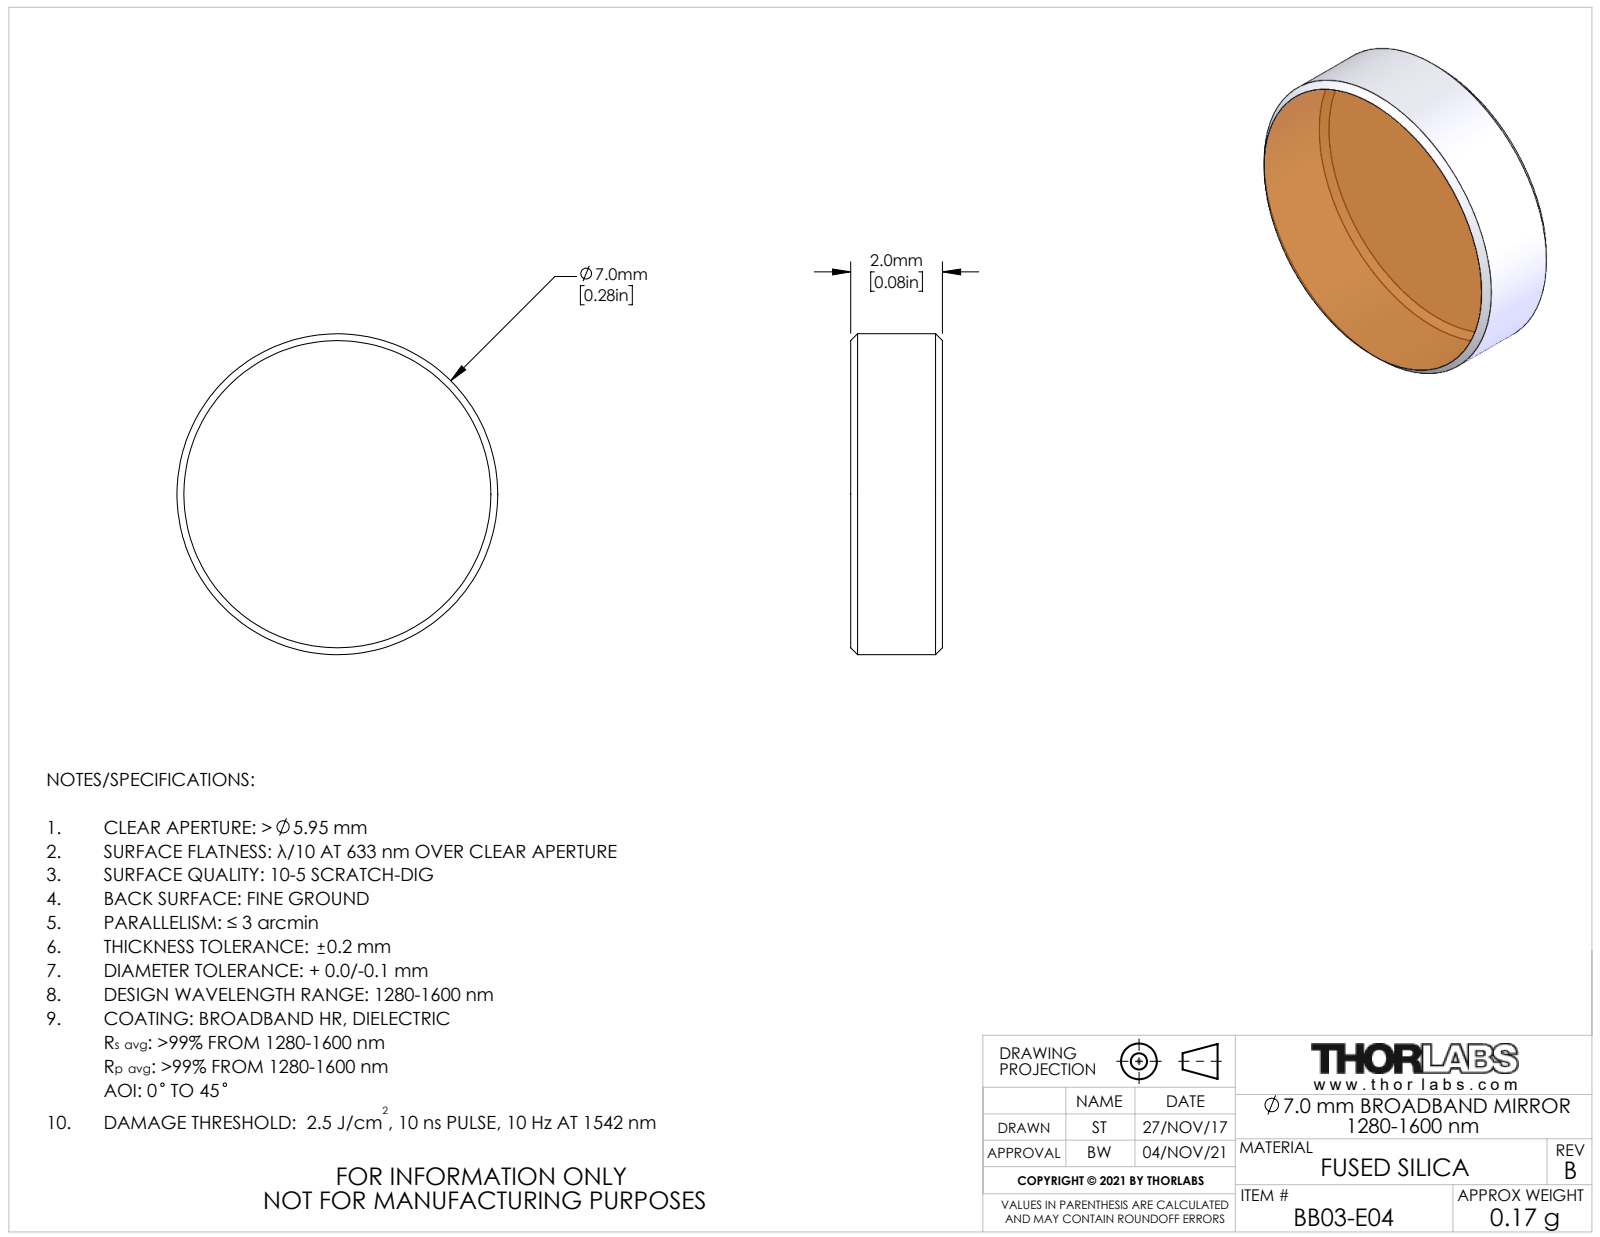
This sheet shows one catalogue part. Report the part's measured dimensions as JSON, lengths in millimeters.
{"part_name": "TTN146940-E0W", "step_written_by": "SolidWorks 2016 (CONFIG_CONTROL_DESIGN)", "units": "millimeters", "bodies": {"solids": 1, "faces": 8, "planar": 2, "cylindrical": 2, "other": 4}, "overall_size": [7, 7, 2], "volume_mm3": 76, "surface_area_mm2": 117, "round_bosses_or_shafts": [[7, 1]], "face_to_face_distances": [2]}
